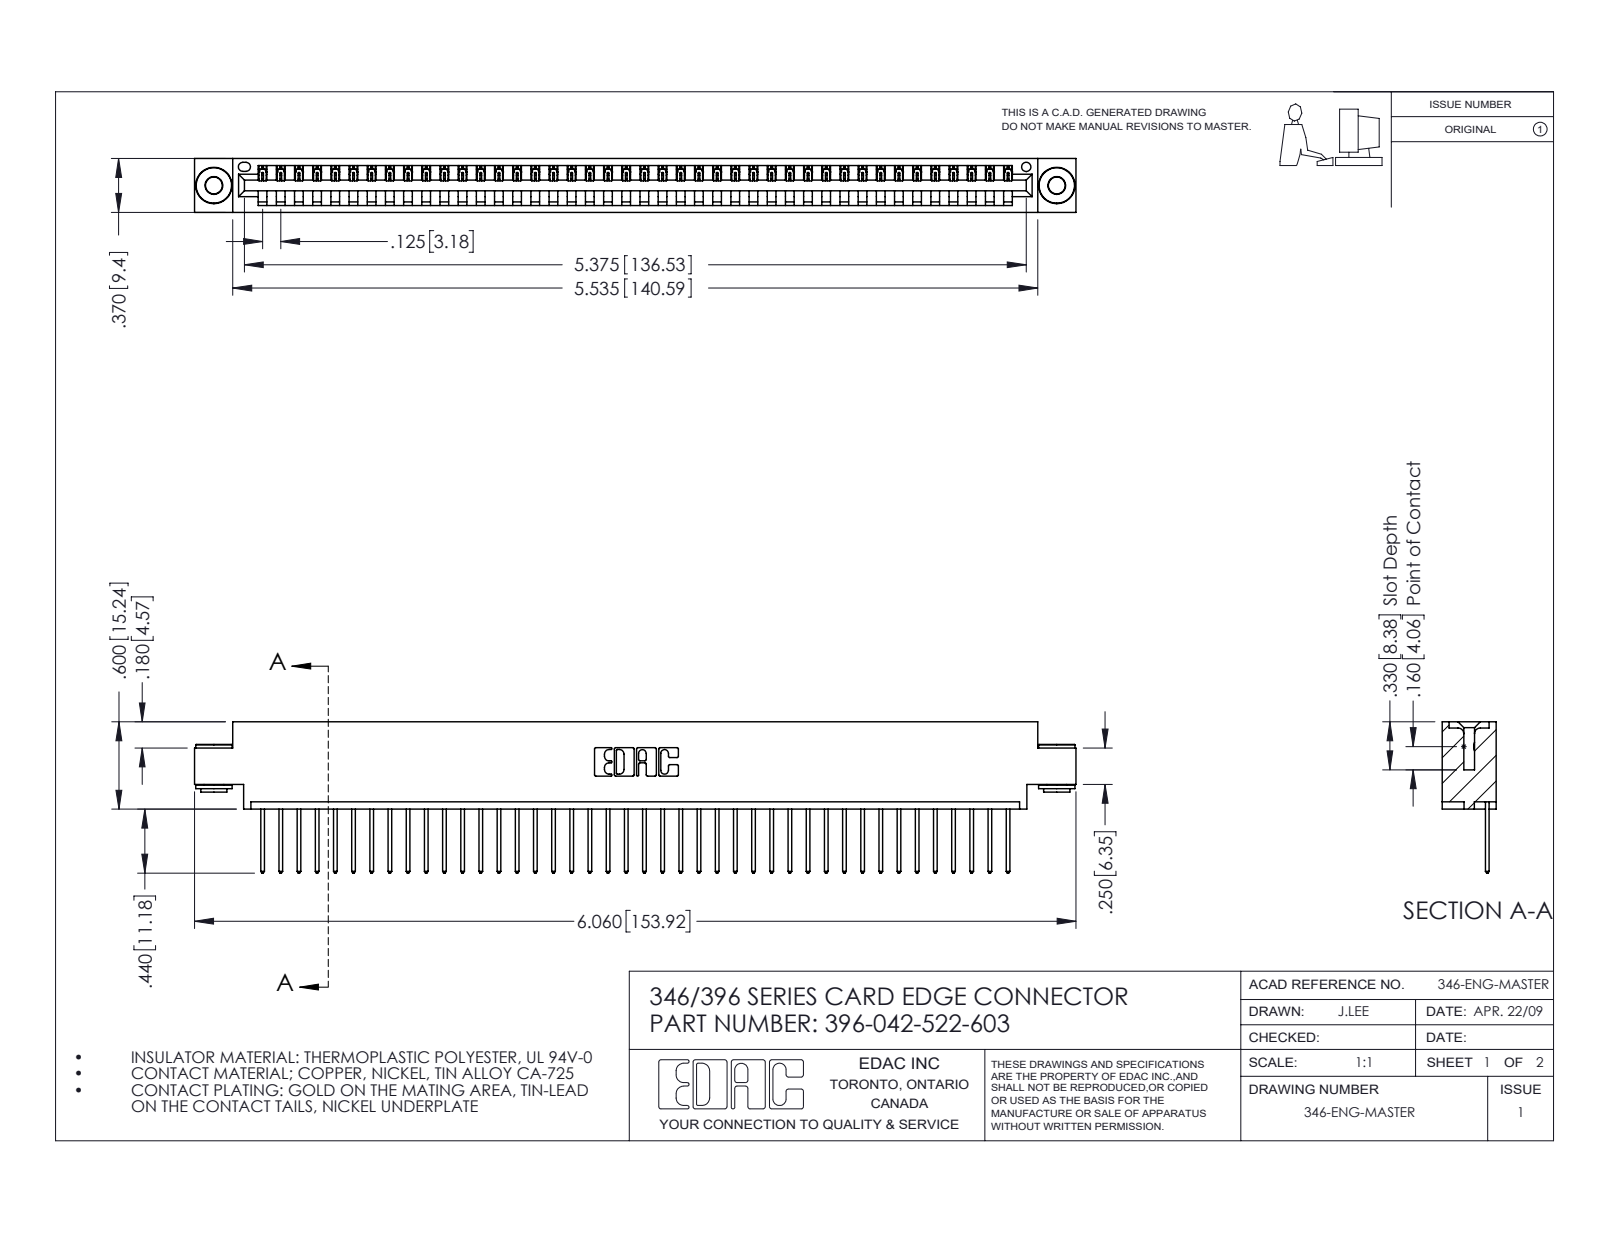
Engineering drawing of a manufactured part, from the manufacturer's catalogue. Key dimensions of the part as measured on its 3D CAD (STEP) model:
Part name (STEP PRODUCT): 346 Part_0.170 Offset - 0.156 Dia-TH; 396-042-522-603; 345-292-001_345-293-122; 345-250-002_345-250-002-102
STEP written by: SolidWorks 2016 (CONFIG_CONTROL_DESIGN)
Units: inches
Bodies: 45 solids, 2600 faces (1770 planar, 822 cylindrical, 8 other)
Overall size (bounding box): 6.06 × 1.04 × 0.37
Volume: 0.891 in³ · Surface area: 29.12 in²
Round holes (diameter × count): ⌀0.116 ×2, ⌀0.156 ×2, ⌀0.064 ×1
Round bosses / shafts (diameter × count): ⌀0.25 ×2, ⌀0.18 ×2, ⌀0.136 ×2
Partial cylindrical surfaces — rounded edges, fillets, slot ends (radius × count): R0.006 ×84, R0.01 ×84, R0.01 ×22, R0.007 ×6, R0.031 ×6, R0.026 ×3, R0.031 ×2, R0.04 ×2
Main face-to-face distances: 0.048, 0.322, 0.37, 0.25, 0.025, 0.072, 0.298, 0.148, 0.222, 0.1
Hole centre spacings: 0.246, 5.586, 5.795
